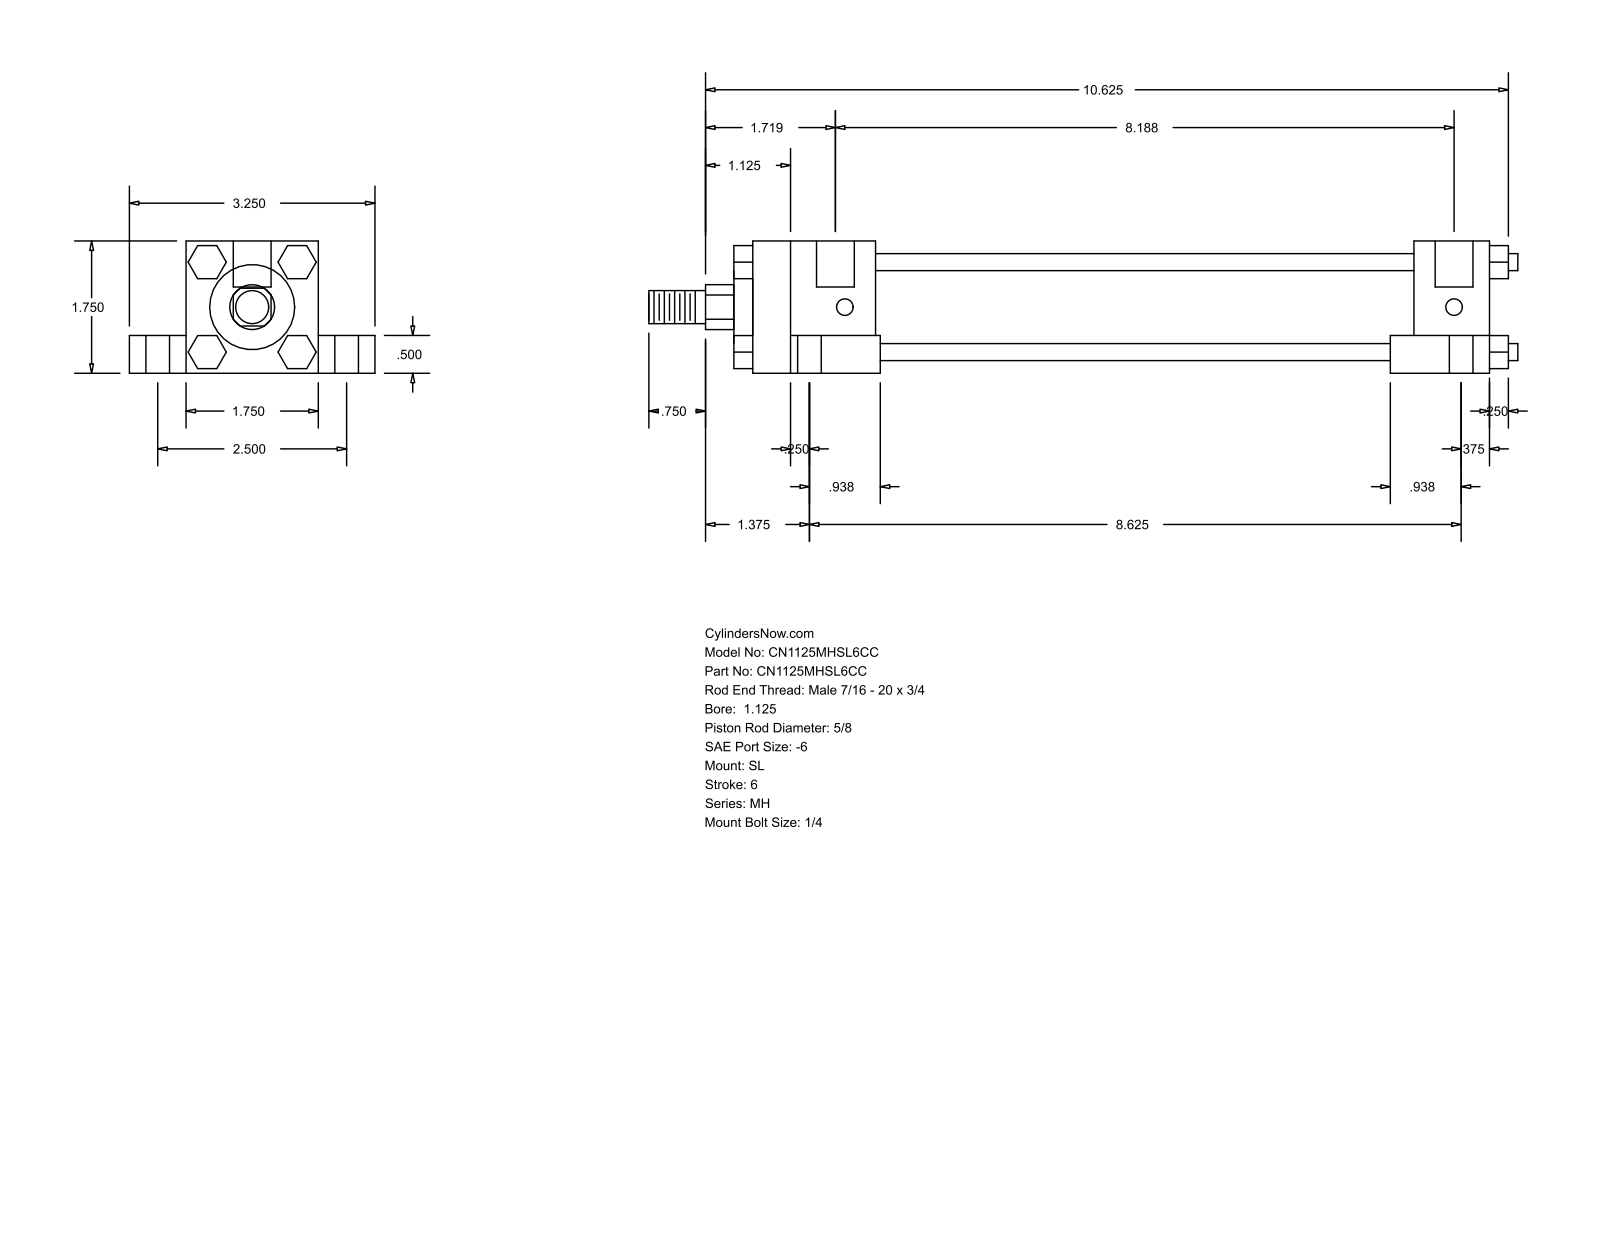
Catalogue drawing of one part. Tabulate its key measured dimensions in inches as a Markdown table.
| quantity | value |
| --- | --- |
| part name | MH_SL__0112_0.625 |
| STEP written by | GSSL Pune (CONFIG_CONTROL_DESIGN) |
| units | inches |
| bodies | 0 solids, 150 faces (114 planar, 36 cylindrical, 0 other) |
| overall size | 11.5 × 3.25 × 1.75 |
| round holes (diameter × count) | 0.219 × 4, 0.313 × 4, 0.563 × 4, 0.5 × 2 |
| round bosses / shafts (diameter × count) | 0.225 × 4, 1.375 × 1, 1.125 × 1, 0.625 × 1, 0.437 × 1 |
| partial cylindrical surfaces (radius × count) | 0.297 × 1 |
| main face-to-face distances | 1.75, 1.25, 0.75, 0.5, 2.5, 0.437, 1.875, 1, 7.125, 8.125 |
| hole center spacings | 1.254, 1.269, 1.296, 2.5, 8.063, 8.252, 8.375, 8.499 |
